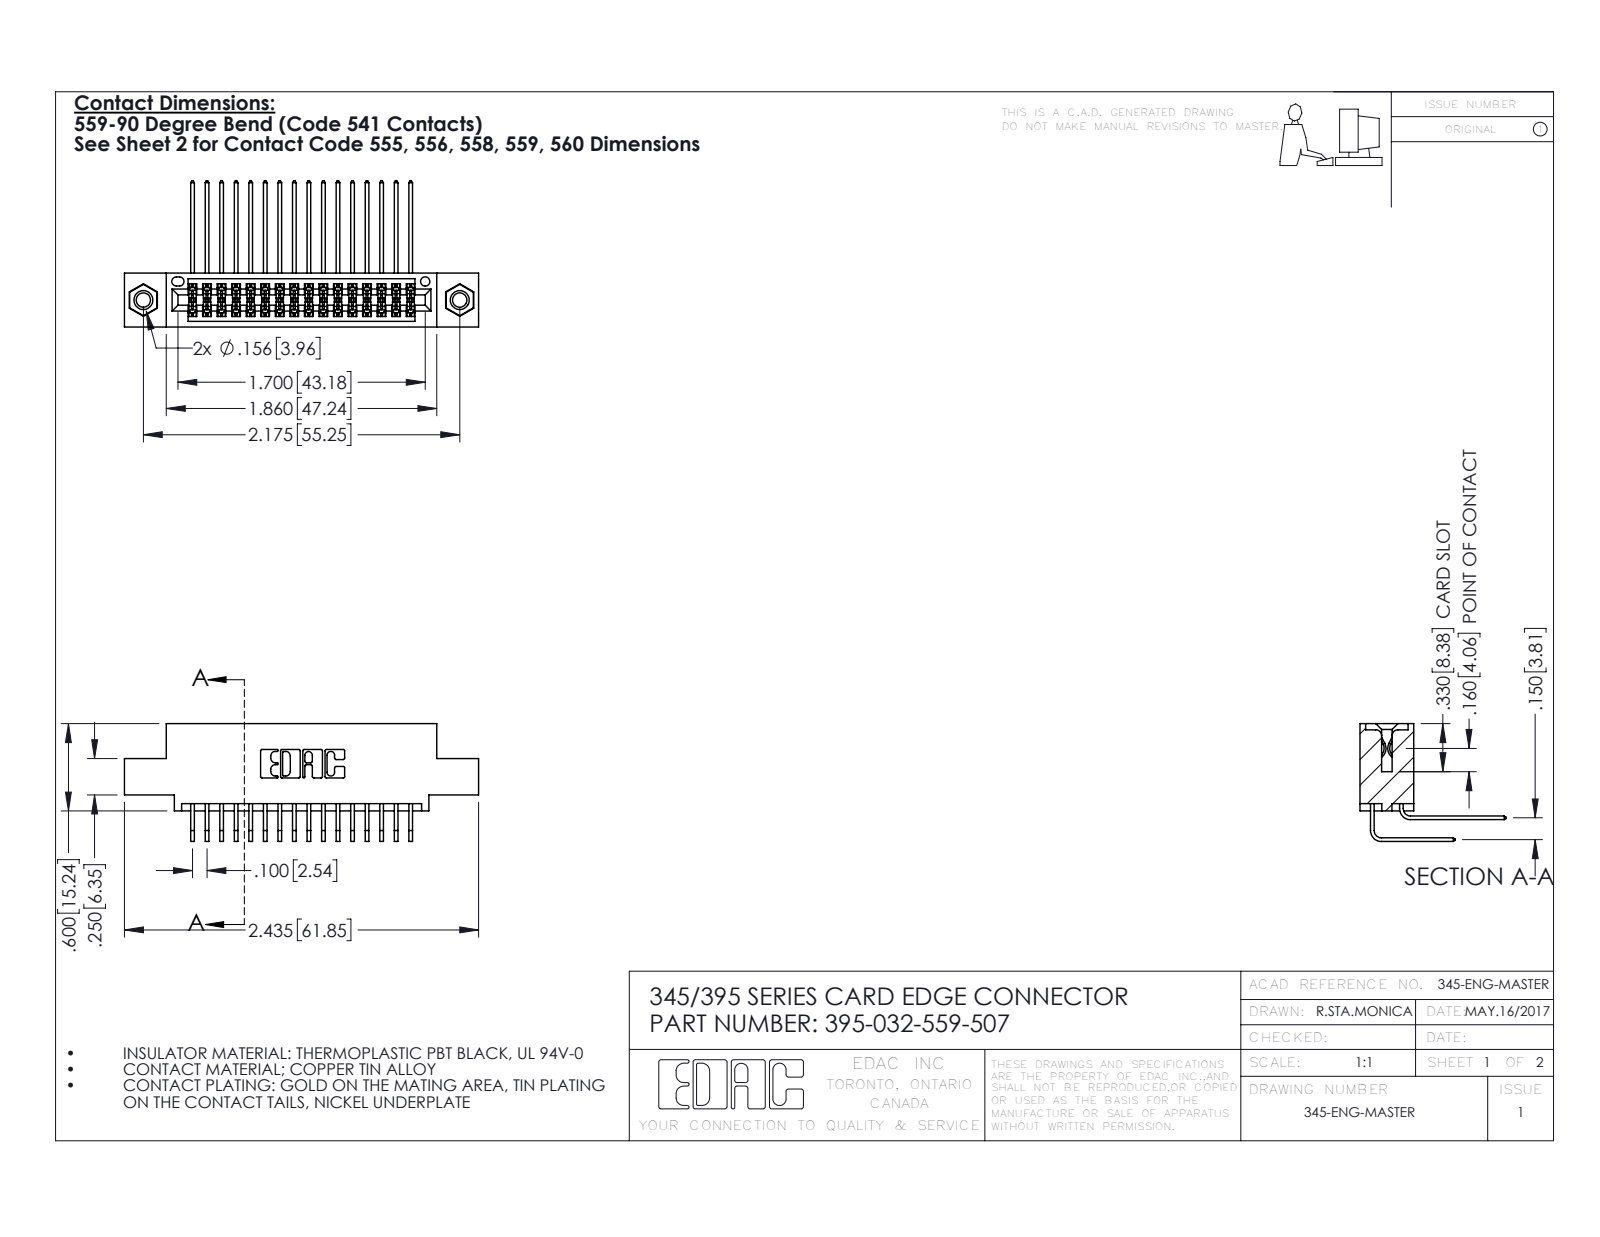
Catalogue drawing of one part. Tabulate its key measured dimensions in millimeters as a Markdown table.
| quantity | value |
| --- | --- |
| part name | 345-292-001_559 Tail - 2; 395-032-559-507; 345 Part_0.110 Offset - 0.156 Dia-TI; 345-292-001_558 559 Tail - 1 (+1 more) |
| STEP written by | SolidWorks 2016 (CONFIG_CONTROL_DESIGN) |
| units | millimeters |
| bodies | 35 solids, 1854 faces (1236 planar, 602 cylindrical, 16 other) |
| overall size | 61.8 × 25.5 × 20.5 |
| volume | 5 870 mm³ |
| surface area | 9 155 mm² |
| round holes (diameter × count) | 2.5 × 2, 3.2 × 2, 4 × 2, 1.6 × 1 |
| round bosses / shafts (diameter × count) | 3.9 × 2 |
| partial cylindrical surfaces (radius × count) | 0.2 × 49, 0.3 × 22, 0.2 × 6, 0.8 × 6, 0.7 × 3, 0.4 × 2, 0.5 × 2, 0.6 × 2 |
| main face-to-face distances | 1.8, 7.6, 5.1, 9.4, 2.5, 6.9, 0.6, 5.7, 3.8, 4.4 |
| hole center spacings | 6.9, 49.3, 55.2 |
